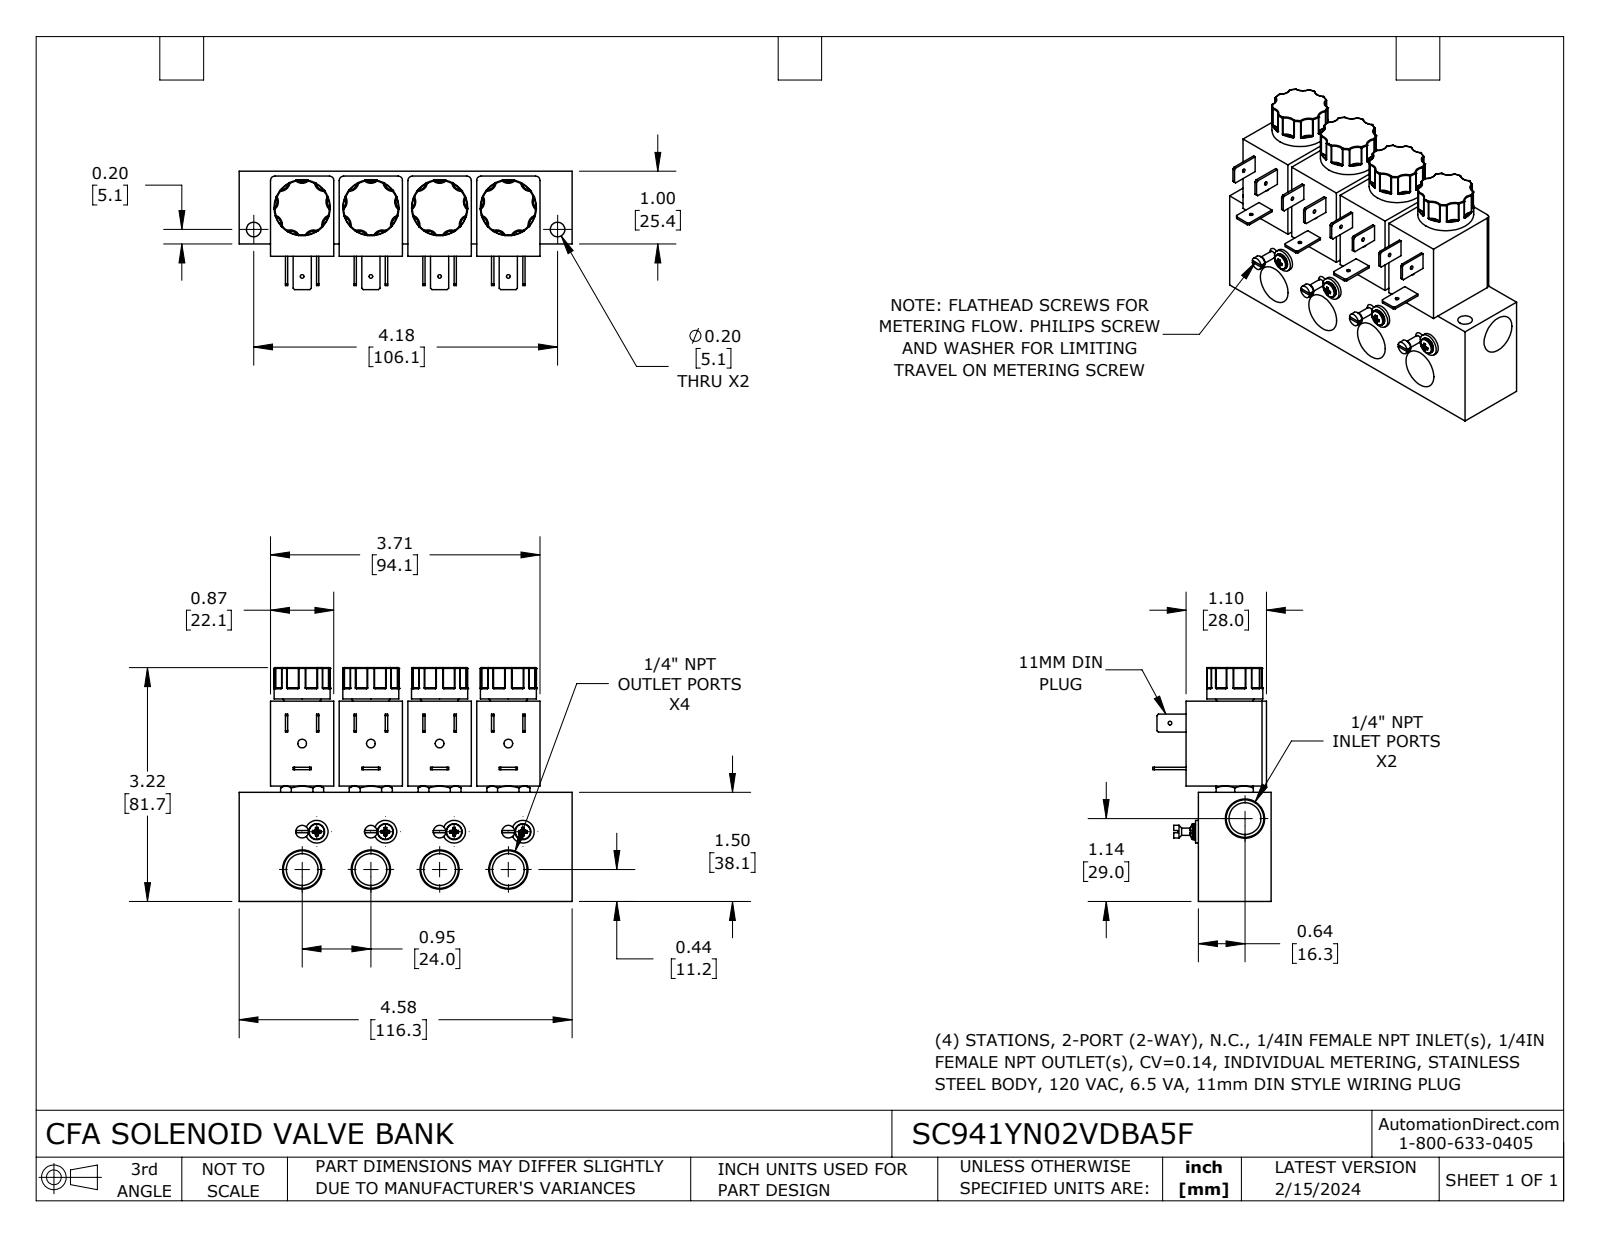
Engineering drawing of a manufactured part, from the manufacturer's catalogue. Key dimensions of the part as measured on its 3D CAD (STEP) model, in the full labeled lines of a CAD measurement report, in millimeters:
Part name (STEP PRODUCT): SC941YN02VDBA5F
STEP written by: SolidWorks 2023 (CONFIG_CONTROL_DESIGN)
Units: millimetres
Bodies: 1 solid, 1098 faces (284 planar, 260 cylindrical, 554 other)
Overall size (bounding box): 116.3 × 81.7 × 41.3
Volume: 188 300 mm³ · Surface area: 44 010 mm²
Round holes (diameter × count): ⌀1.3 ×5, ⌀11.1 ×5, ⌀3 ×4, ⌀5.1 ×2
Round bosses / shafts (diameter × count): ⌀19.6 ×4, ⌀7.9 ×4, ⌀5.6 ×4, ⌀4.4 ×4, ⌀2.5 ×4
Partial cylindrical surfaces — rounded edges, fillets, slot ends (radius × count): R0.3 ×72, R3.4 ×28, R1.5 ×8, R3.4 ×8
Main face-to-face distances: 25.4, 24, 29.7, 4.3, 48, 22.1, 46.1, 38.1, 1.7, 23.7
Hole centre spacings: 24, 44, 50.1, 24, 48, 48, 72, 50.1
